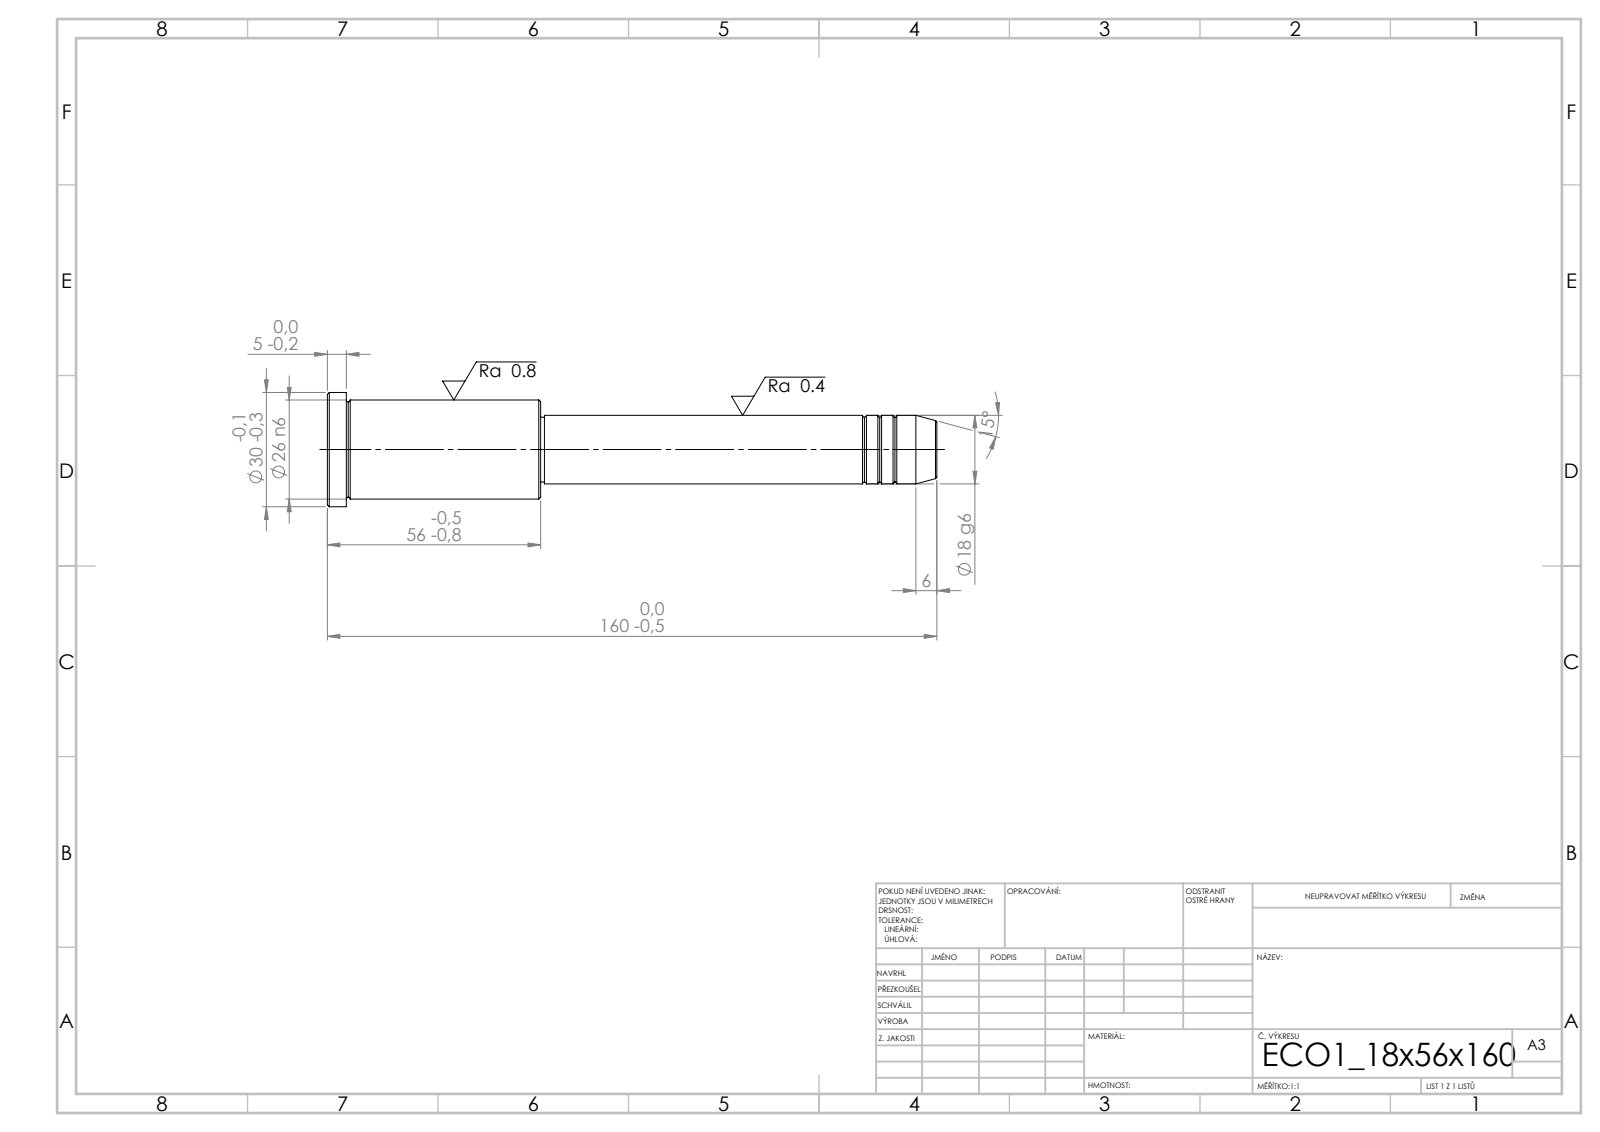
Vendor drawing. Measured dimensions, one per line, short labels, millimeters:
written by: SolidWorks 2019 (CONFIG_CONTROL_DESIGN)
unit: mm
bodies: 1 solid, 43 faces (5 planar, 14 cylindrical, 24 other)
size: 160 × 30 × 30
volume: 56 713 mm³; area: 11 965 mm²
bosses: 1× ⌀30, 1× ⌀26, 1× ⌀18, 1× ⌀17
face distances: 56, 51, 5, 104, 155, 160, 103, 1, 52, 57
